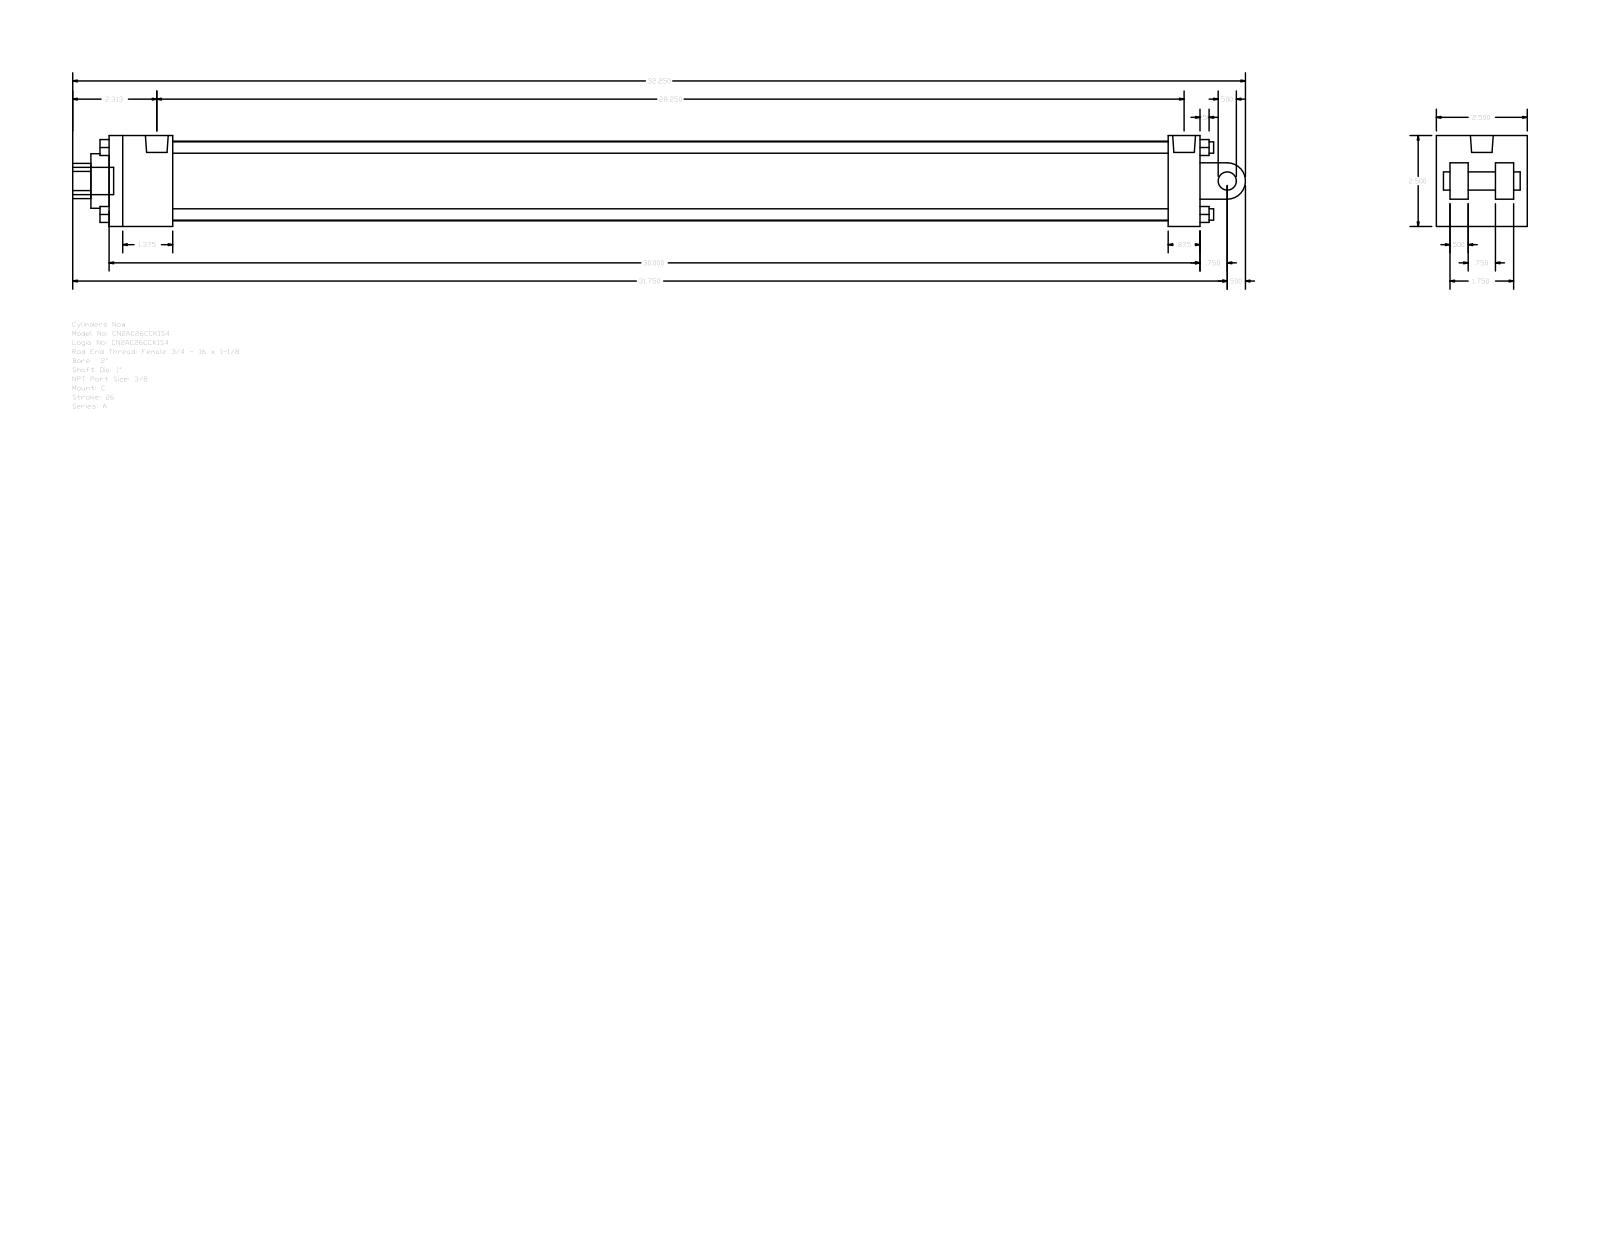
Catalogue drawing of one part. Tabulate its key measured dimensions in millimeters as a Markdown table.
| quantity | value |
| --- | --- |
| part name | A_C__0200_1 |
| STEP written by | GSSL Pune (CONFIG_CONTROL_DESIGN) |
| units | millimeters |
| bodies | 0 solids, 135 faces (102 planar, 33 cylindrical, 0 other) |
| overall size | 819.15 × 63.5 × 63.5 |
| round holes (diameter × count) | 5.56 × 2, 15.93 × 1, 25.4 × 1, 38.1 × 1, 55.63 × 1 |
| round bosses / shafts (diameter × count) | 7.94 × 4, 5.56 × 2, 19.05 × 1, 15.93 × 1, 12.7 × 1 |
| partial cylindrical surfaces (radius × count) | 12.29 × 1, 12.7 × 1 |
| main face-to-face distances | 63.5, 762, 44.45, 12.7, 9.52, 41.28, 717.55, 739.77, 695.32, 22.23 |
| hole center spacings | 3.98 |
